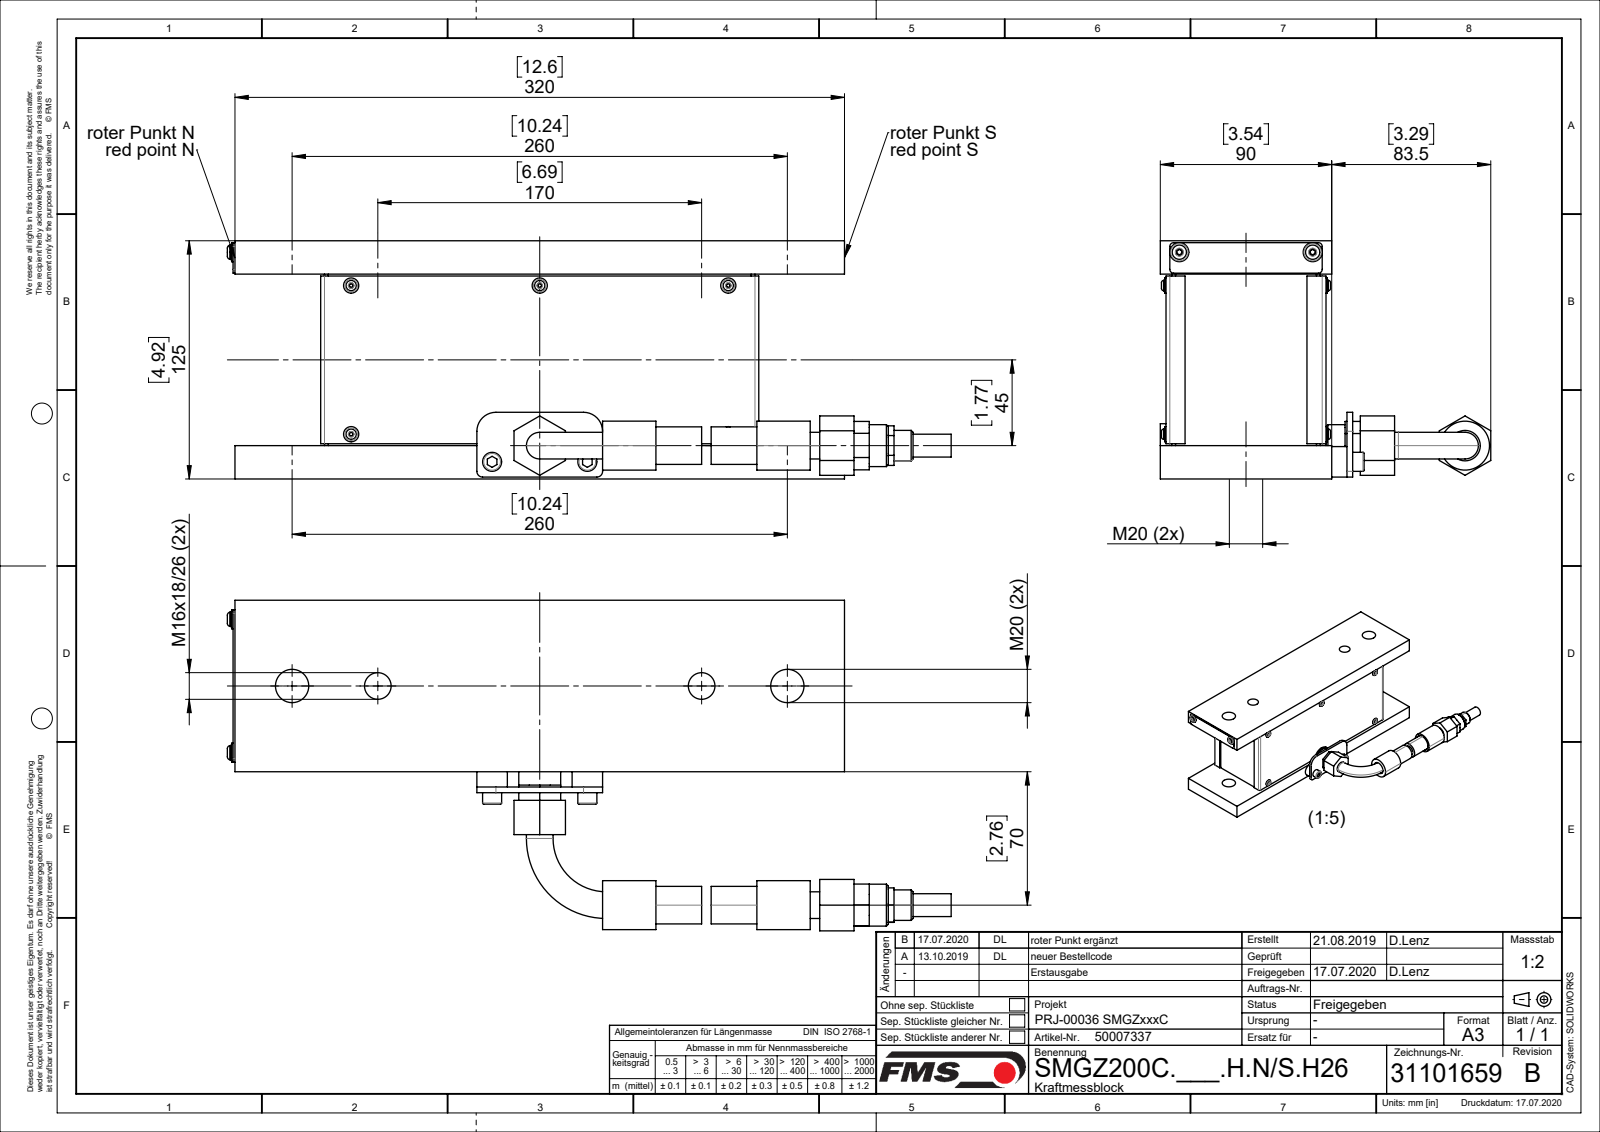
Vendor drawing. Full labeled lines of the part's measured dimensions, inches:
Part name (STEP PRODUCT): 31101659_stp; Kabelverschraubung_M16x1-5_kurz_ohne Huelse_01; 31101613_01; Steuerkabel_12x20 (+8 more)
STEP written by: SolidWorks 2018 (CONFIG_CONTROL_DESIGN)
Units: inches
Bodies: 40 solids, 1085 faces (305 planar, 612 cylindrical, 168 other)
Overall size (bounding box): 14.961 × 6.831 × 4.921
Volume: 166.5 in³ · Surface area: 655.9 in²
Round holes (diameter × count): ⌀0.157 ×6, ⌀0.098 ×5, ⌀0.213 ×5, ⌀0.551 ×4, ⌀0.394 ×3, ⌀0.13 ×2, ⌀0.165 ×2, ⌀0.197 ×2, ⌀0.256 ×2, ⌀0.276 ×2, ⌀0.295 ×2, ⌀0.354 ×2
Round bosses / shafts (diameter × count): ⌀0.315 ×5, ⌀0.118 ×5, ⌀0.394 ×4, ⌀0.866 ×2, ⌀0.776 ×2, ⌀0.669 ×2, ⌀0.63 ×2, ⌀0.61 ×2
Partial cylindrical surfaces — rounded edges, fillets, slot ends (radius × count): R0.011 ×60, R0.016 ×24, R0.079 ×16, R0.039 ×12, R0.118 ×2, R0.394 ×2, R0.453 ×1
Main face-to-face distances: 0.039, 0.079, 3.189, 3.15, 0.118, 3.228, 3.11, 3.307, 3.071, 3.268
Hole centre spacings: 4.189, 1.772, 3.772, 1.04, 1.378, 1.969, 2.325, 2.969
